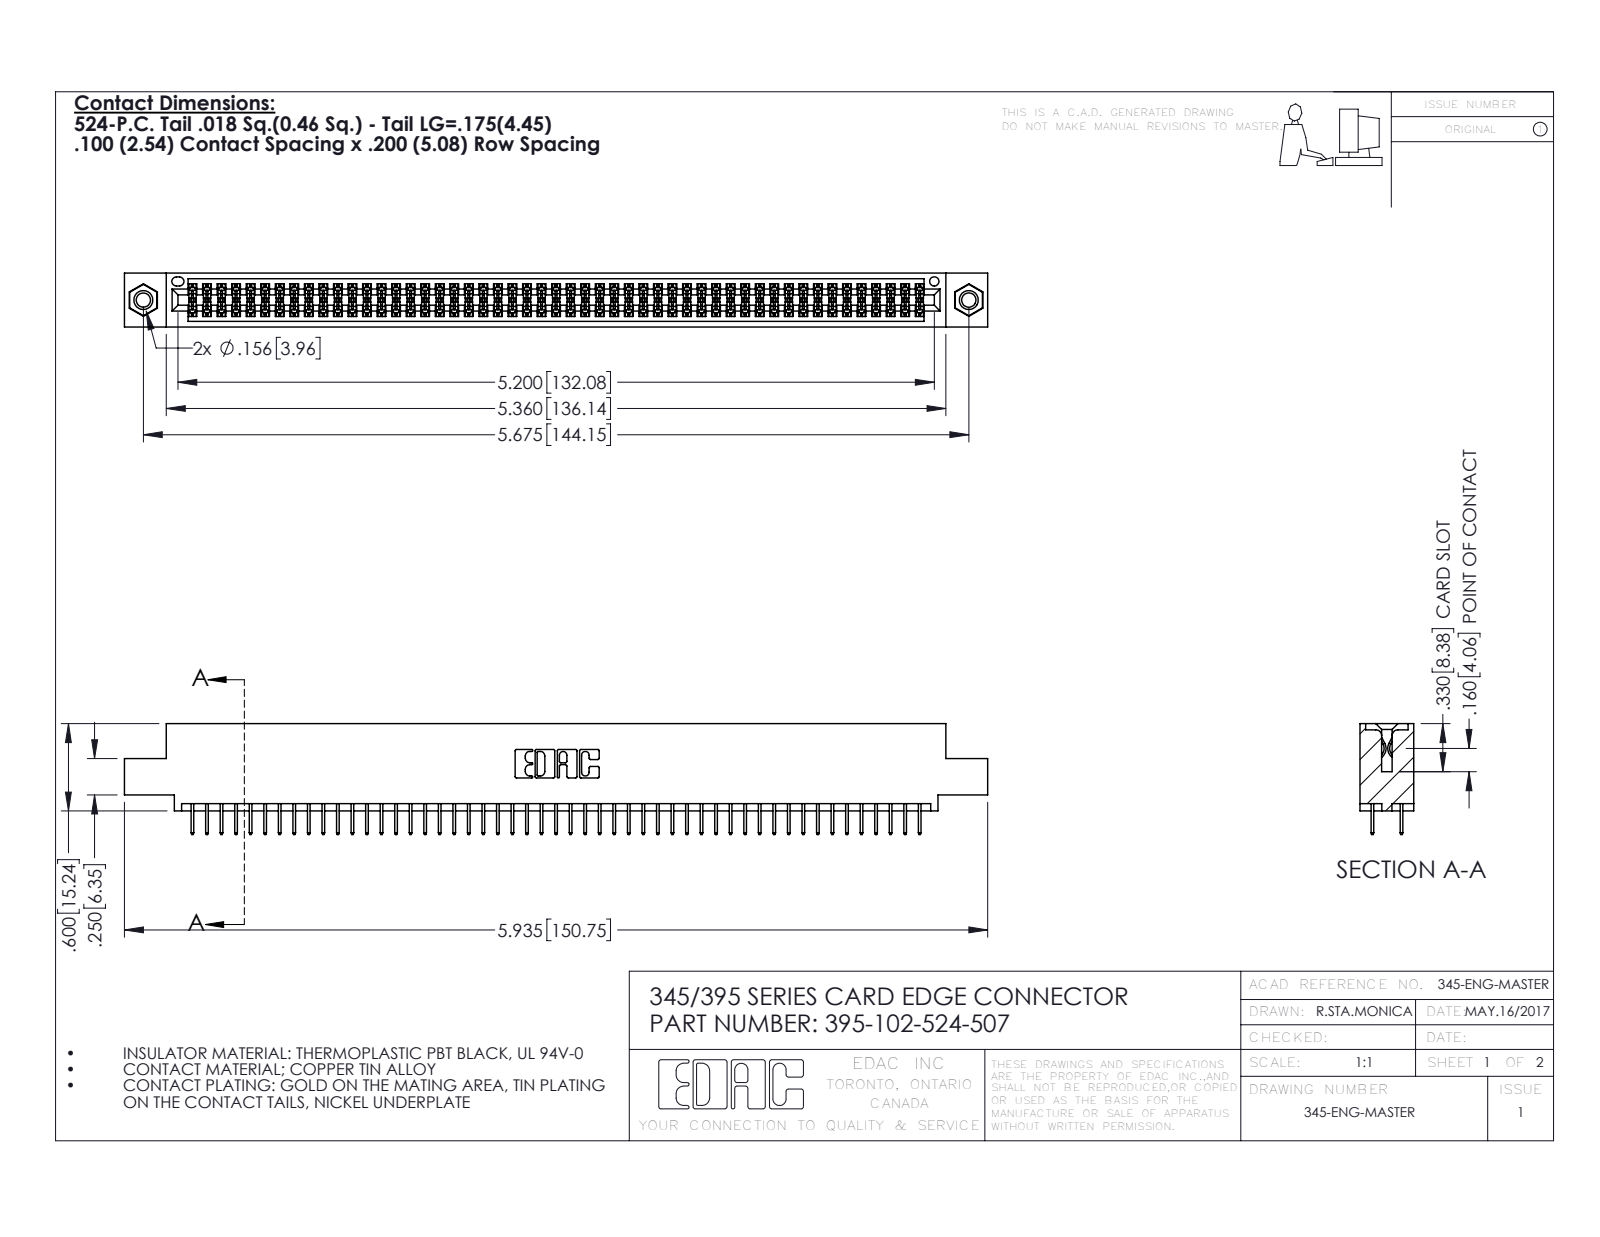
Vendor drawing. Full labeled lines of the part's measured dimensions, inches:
Part name (STEP PRODUCT): 395-102-524-507; 345-292-001_345-293-124; 345 Part_0.110 Offset - 0.156 Dia-TI; 345-250-001_345-250-005-103
STEP written by: SolidWorks 2016 (CONFIG_CONTROL_DESIGN)
Units: inches
Bodies: 105 solids, 5698 faces (4094 planar, 1588 cylindrical, 16 other)
Overall size (bounding box): 5.935 × 0.762 × 0.37
Volume: 0.884 in³ · Surface area: 33.02 in²
Round holes (diameter × count): ⌀0.098 ×2, ⌀0.125 ×2, ⌀0.156 ×2, ⌀0.064 ×1
Round bosses / shafts (diameter × count): ⌀0.155 ×2
Partial cylindrical surfaces — rounded edges, fillets, slot ends (radius × count): R0.006 ×153, R0.01 ×22, R0.007 ×6, R0.031 ×6, R0.026 ×3, R0.014 ×2, R0.019 ×2, R0.022 ×2
Main face-to-face distances: 0.072, 0.298, 0.2, 0.37, 0.098, 0.272, 0.025, 0.225, 0.072, 0.175
Hole centre spacings: 0.27, 5.439, 5.675
